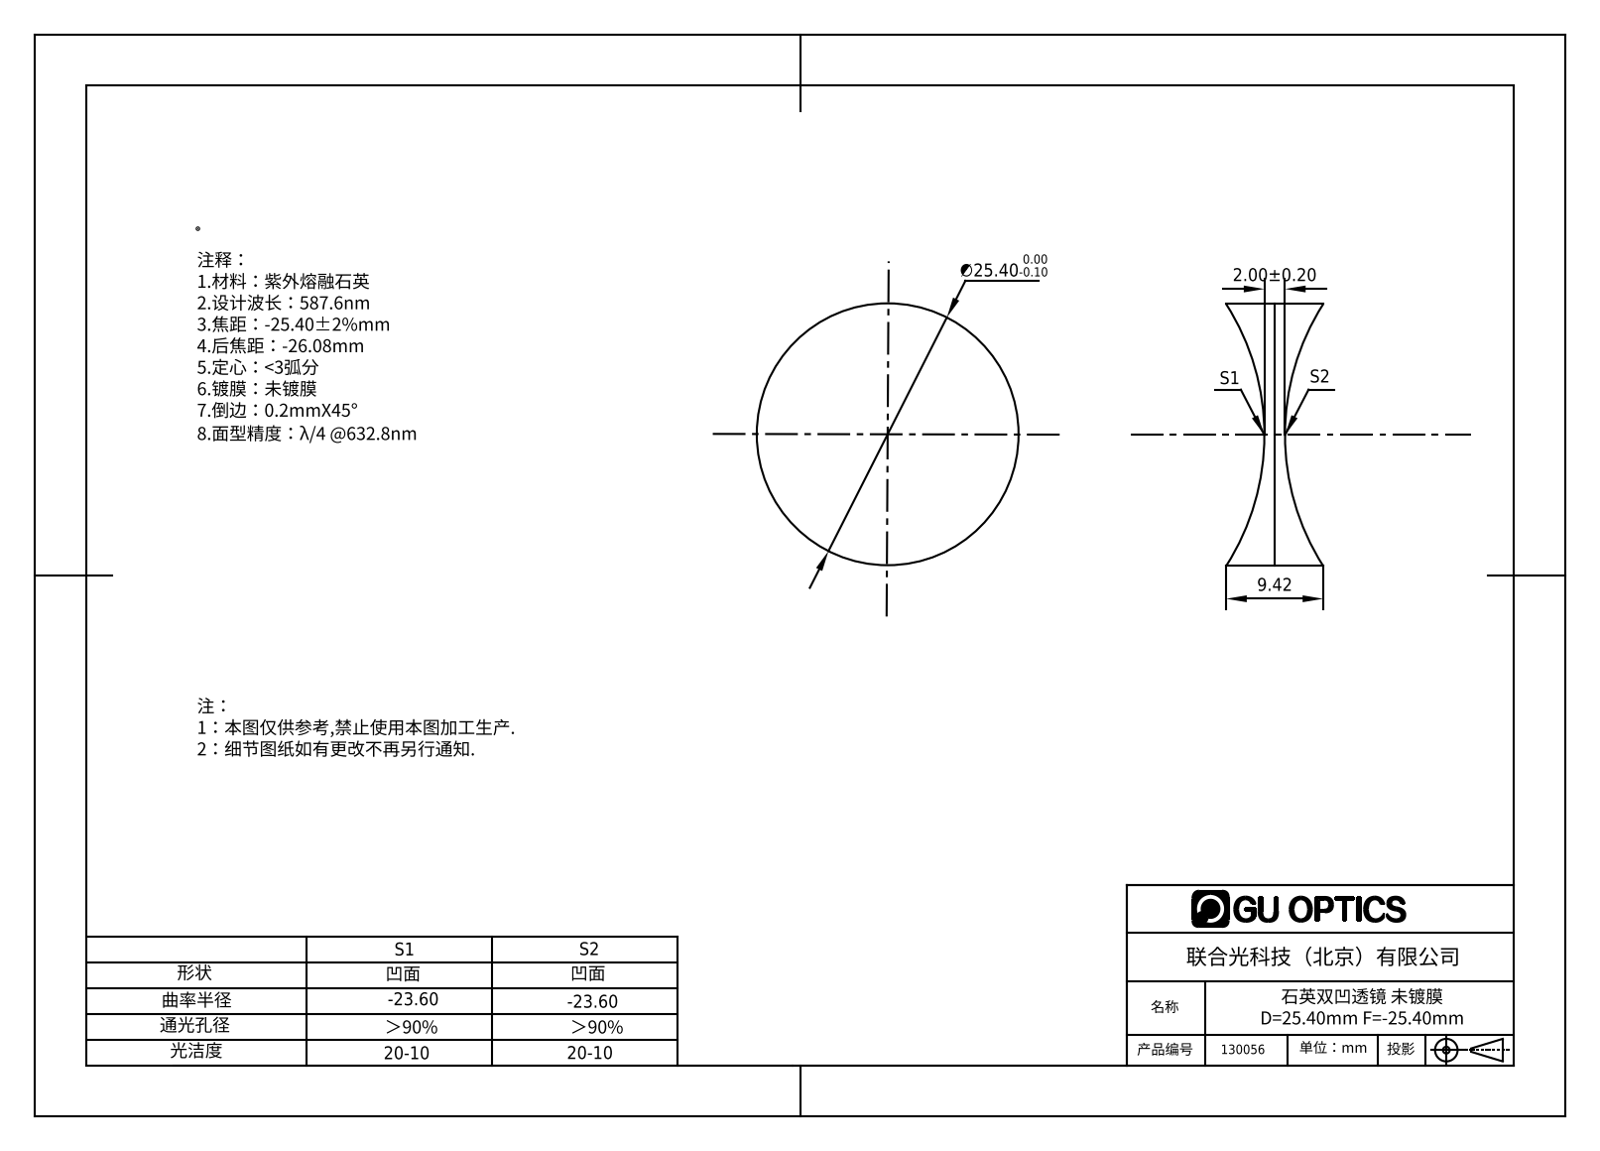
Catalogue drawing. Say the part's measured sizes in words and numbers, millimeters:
The part is named "130056". Its 3-D file was written by "SolidWorks 2016 (AUTOMOTIVE_DESIGN)". It is 1 solid with 6 faces: 0 planar, 2 cylindrical and 4 other. Overall it measures 25.4 by 25.4 by 9.42 millimeters. Its volume is 2 839 cubic millimeters and its surface area 1 851 square millimeters. Round bosses or shafts: 1 of diameter 25.4.
